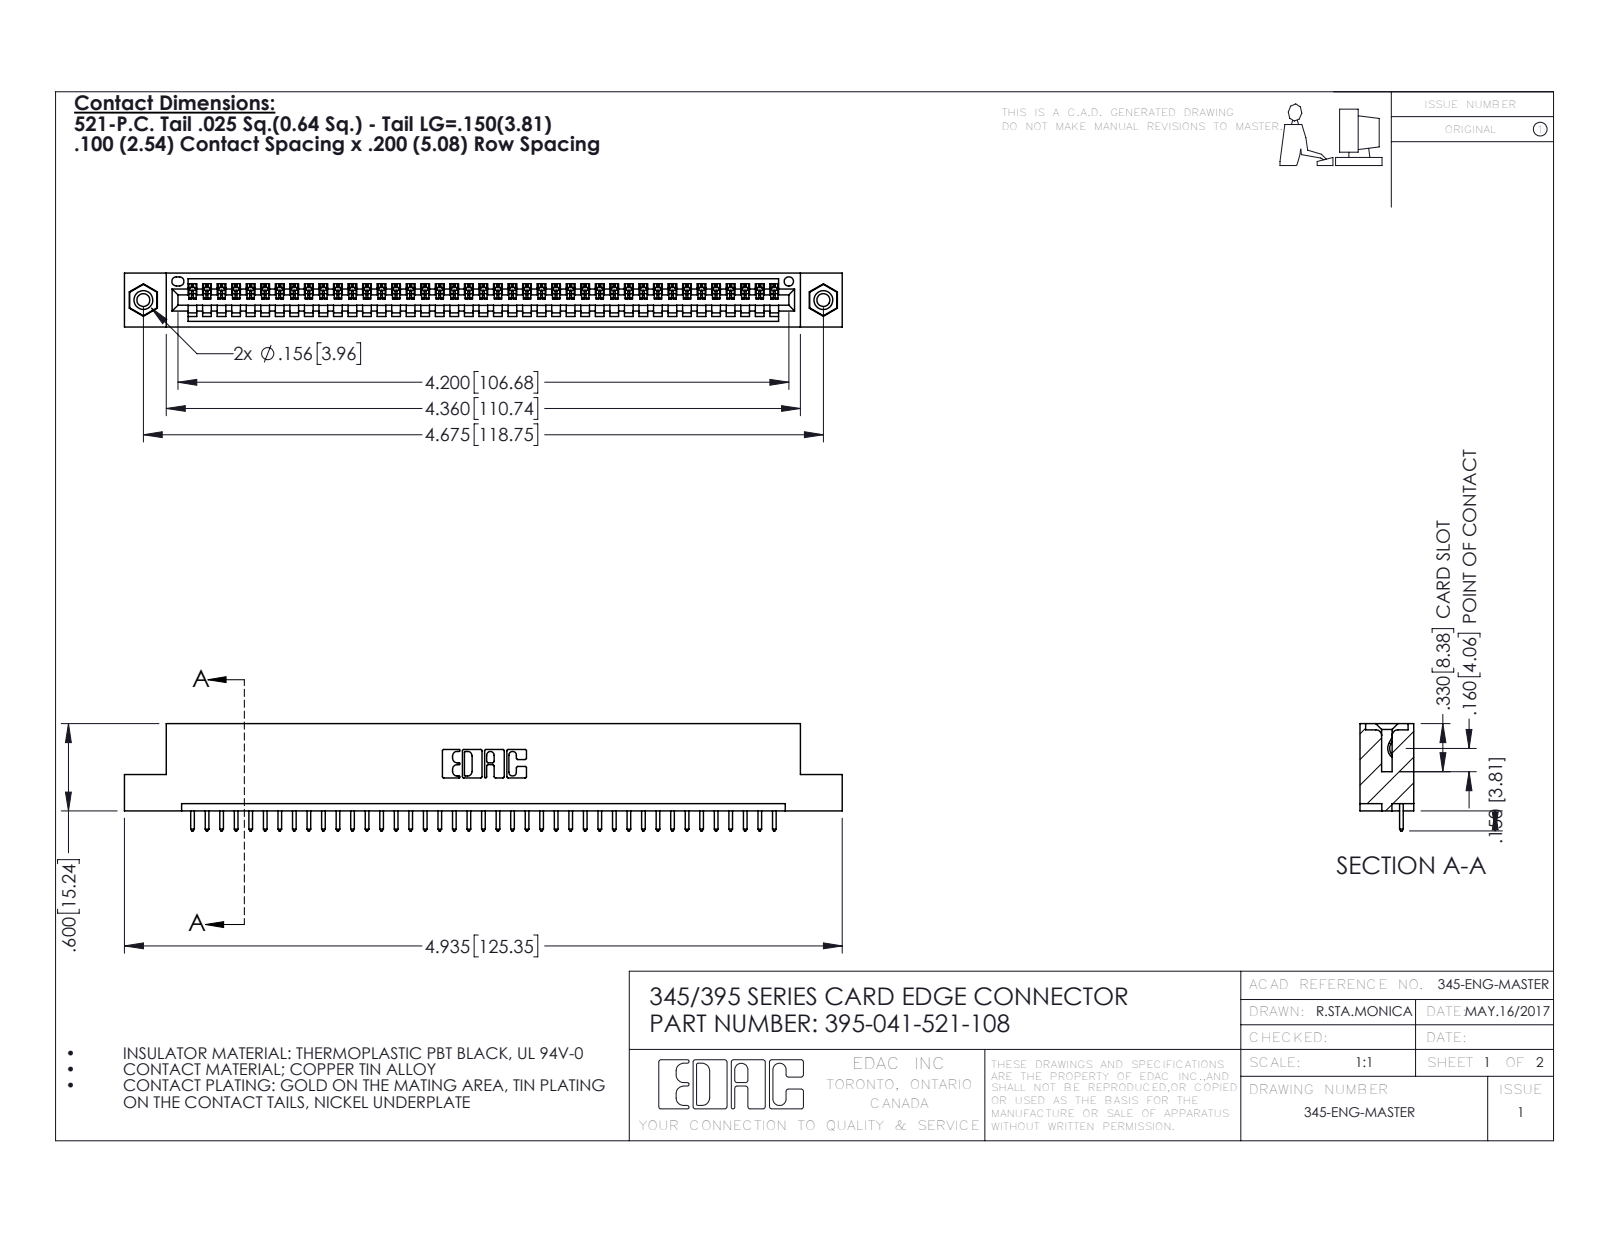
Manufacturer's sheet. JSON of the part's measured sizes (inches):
{"part_name": "345-250-001_345-250-003-102; 345-292-001_345-293-121; 395-041-521-108; 345 Part_Flush Mounting Lugs - 0.156 Dia-TI", "step_written_by": "SolidWorks 2016 (CONFIG_CONTROL_DESIGN)", "units": "inches", "bodies": {"solids": 44, "faces": 2564, "planar": 1752, "cylindrical": 796, "other": 16}, "overall_size": [4.935, 0.737, 0.37], "volume_in3": 0.719, "surface_area_in2": 23.55, "round_holes": [[0.089, 2], [0.125, 2], [0.156, 2], [0.064, 1]], "round_bosses_or_shafts": [[0.155, 2]], "partial_cylinders_radius": [[0.006, 82], [0.01, 82], [0.01, 22], [0.007, 6], [0.031, 6], [0.026, 3], [0.031, 2], [0.04, 2]], "face_to_face_distances": [0.072, 0.298, 0.37, 0.2, 0.098, 0.272, 0.025, 0.225, 0.149, 0.072], "hole_center_spacings": [0.27, 4.439, 4.675]}
